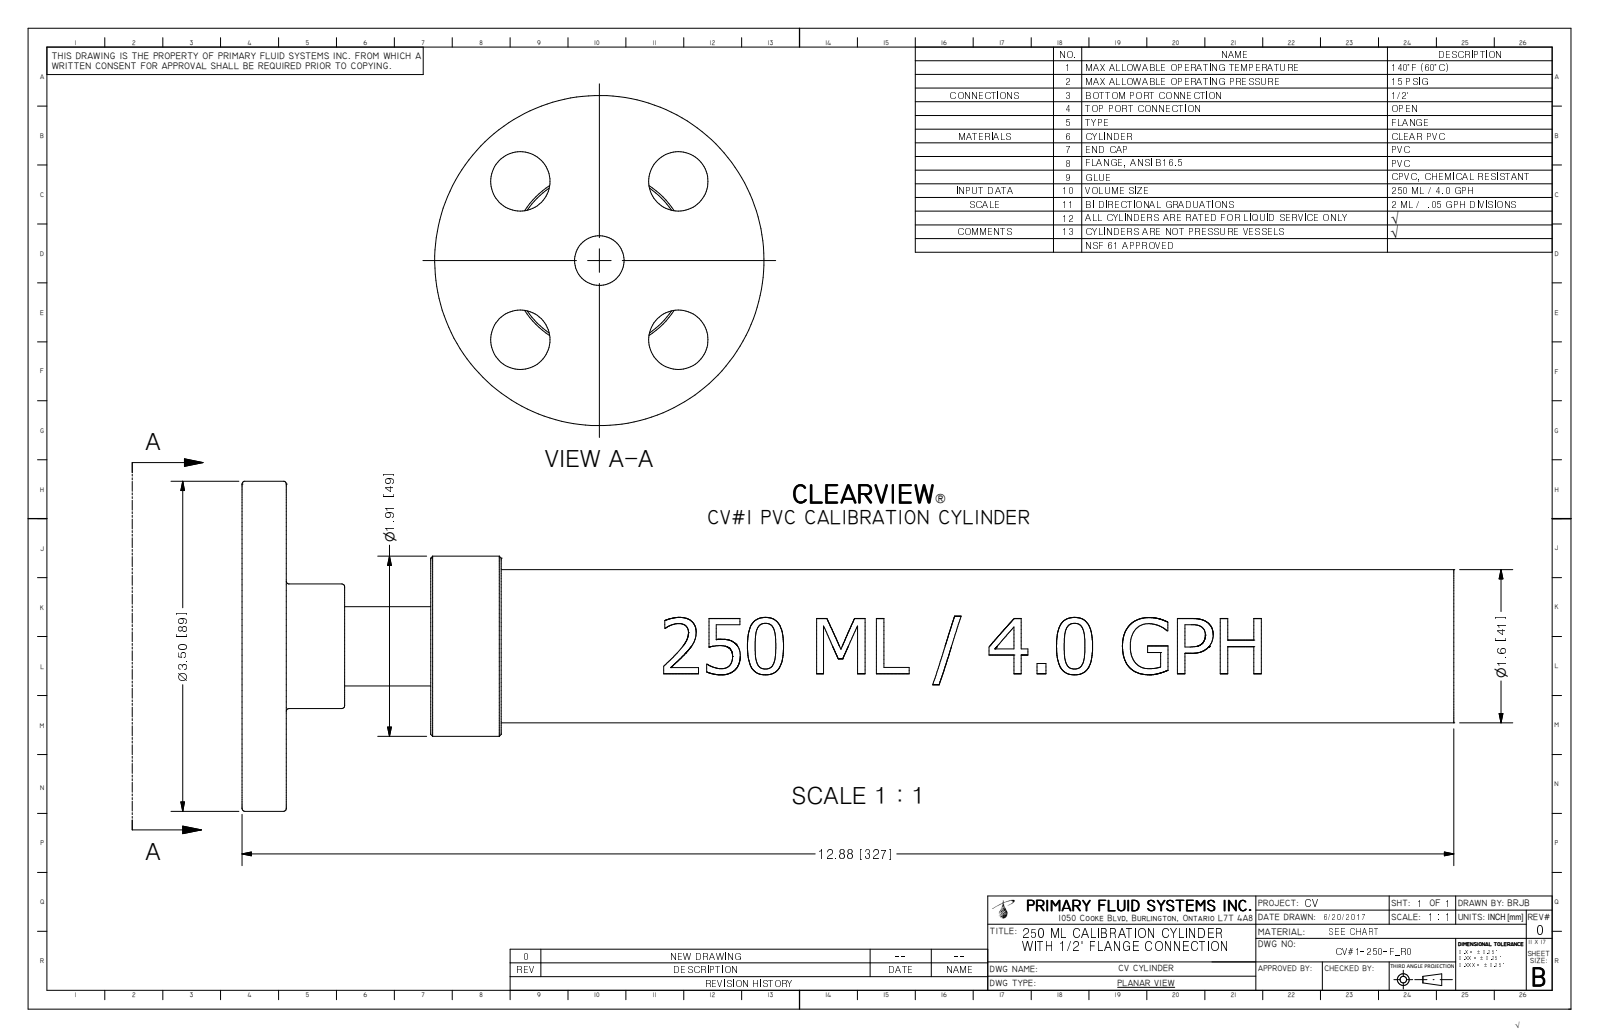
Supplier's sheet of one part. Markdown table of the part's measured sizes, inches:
| quantity | value |
| --- | --- |
| part name | PV#1-250-F_R0 |
| STEP written by | Autodesk Inventor 2009 (AUTOMOTIVE_DESIGN) |
| units | inches |
| bodies | 2 solids, 253 faces (94 planar, 26 cylindrical, 133 other) |
| overall size | 12.88 × 3.5 × 3.5 |
| volume | 9.494 in³ |
| surface area | 157.3 in² |
| round holes (diameter × count) | 0.63 × 4, 0.526 × 1, 1.505 × 1 |
| round bosses / shafts (diameter × count) | 3.5 × 1, 1.91 × 1, 1.625 × 1, 1.32 × 1 |
| partial cylindrical surfaces (radius × count) | 0.811 × 1 |
| main face-to-face distances | 0.47, 2.005, 1.535, 0.915, 1.09, 0.62, 2.755, 2.285, 1.665, 0.75 |
| hole center spacings | 1.188, 1.68, 2.375 |
